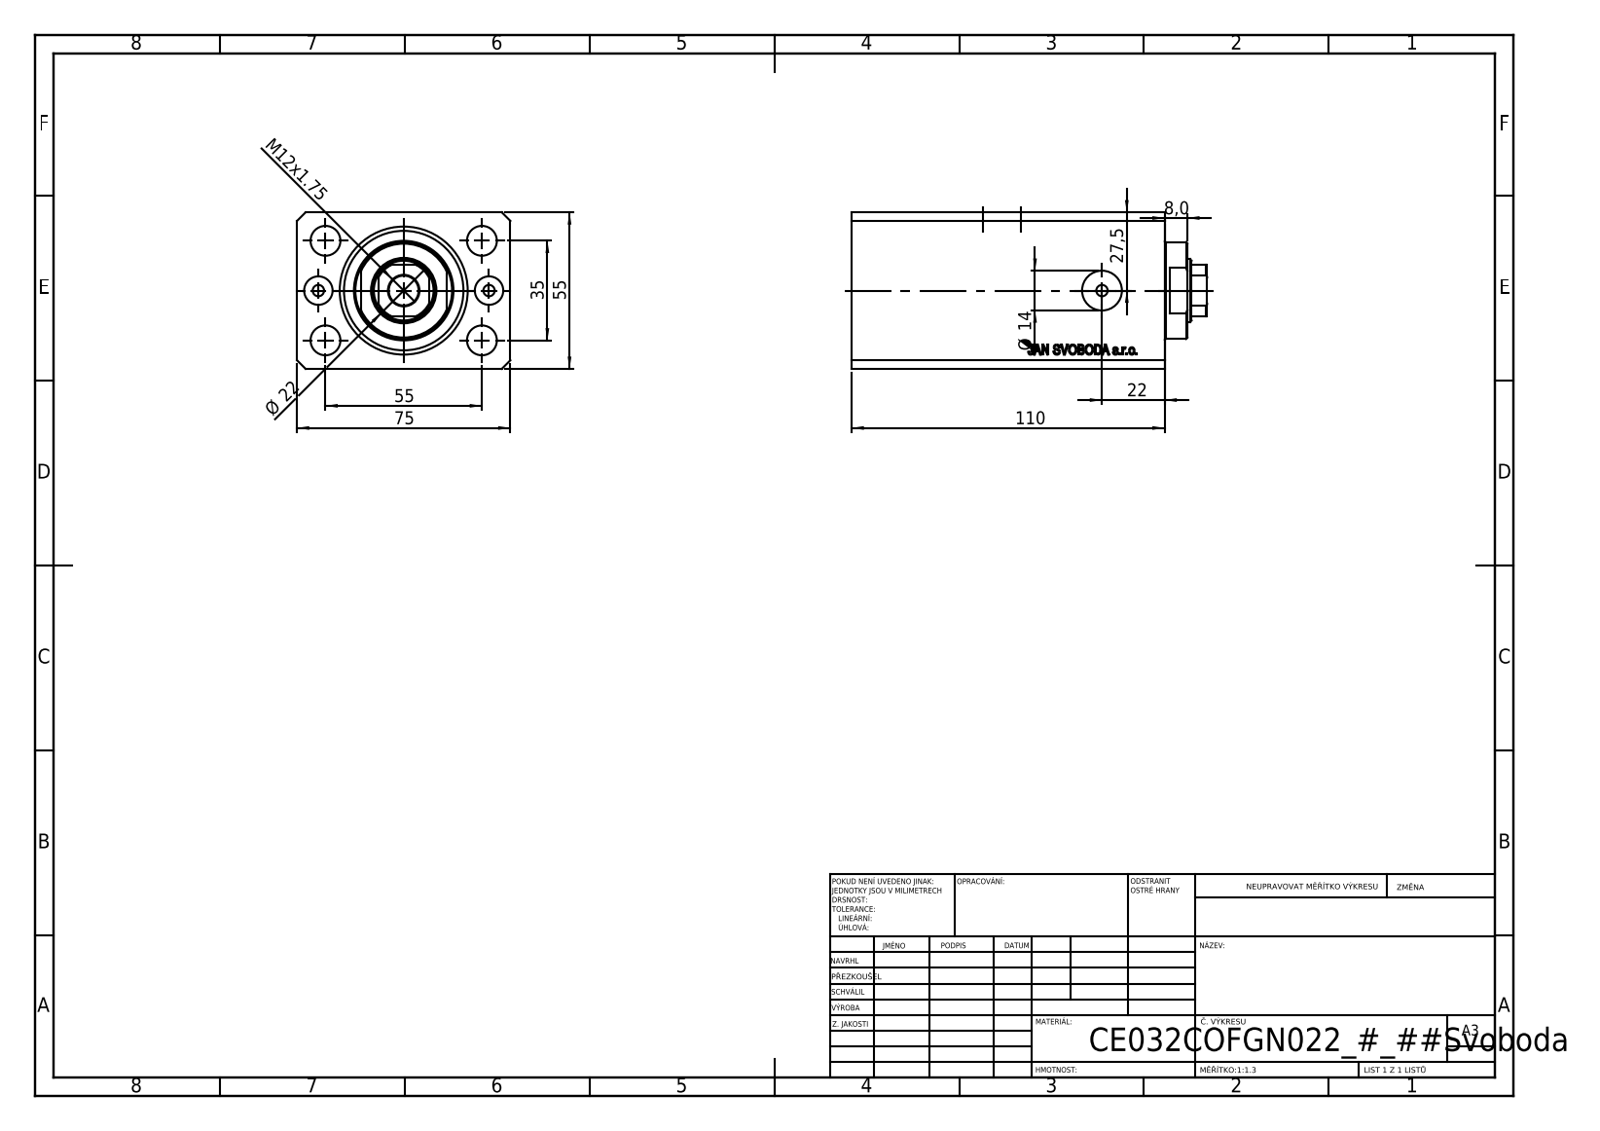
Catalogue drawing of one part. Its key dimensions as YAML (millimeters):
part_name: "V250CE_C_VCP; V250CE_VC_C; V250CE_C_Body"
step_written_by: "SolidWorks 2019 (CONFIG_CONTROL_DESIGN)"
units: millimeters
bodies: {solids: 3, faces: 864, planar: 428, cylindrical: 44, other: 392}
overall_size: [125, 75, 55]
volume: 396706
surface_area: 80864
round_holes:
  - {diameter: 10.5, count: 5}
  - {diameter: 4, count: 4}
  - {diameter: 10, count: 2}
  - {diameter: 14, count: 2}
  - {diameter: 22, count: 1}
  - {diameter: 32, count: 1}
  - {diameter: 45, count: 1}
round_bosses_or_shafts:
  - {diameter: 34, count: 1}
partial_cylinders:
  - {radius: 10.5, count: 1}
face_to_face_distances: [55, 75, 110, 15, 95, 9.9, 85.1, 100.1, 87.66, 108.1]
hole_center_spacings: [17.68, 32.6, 60.1, 30, 35, 55, 65.19, 60]
